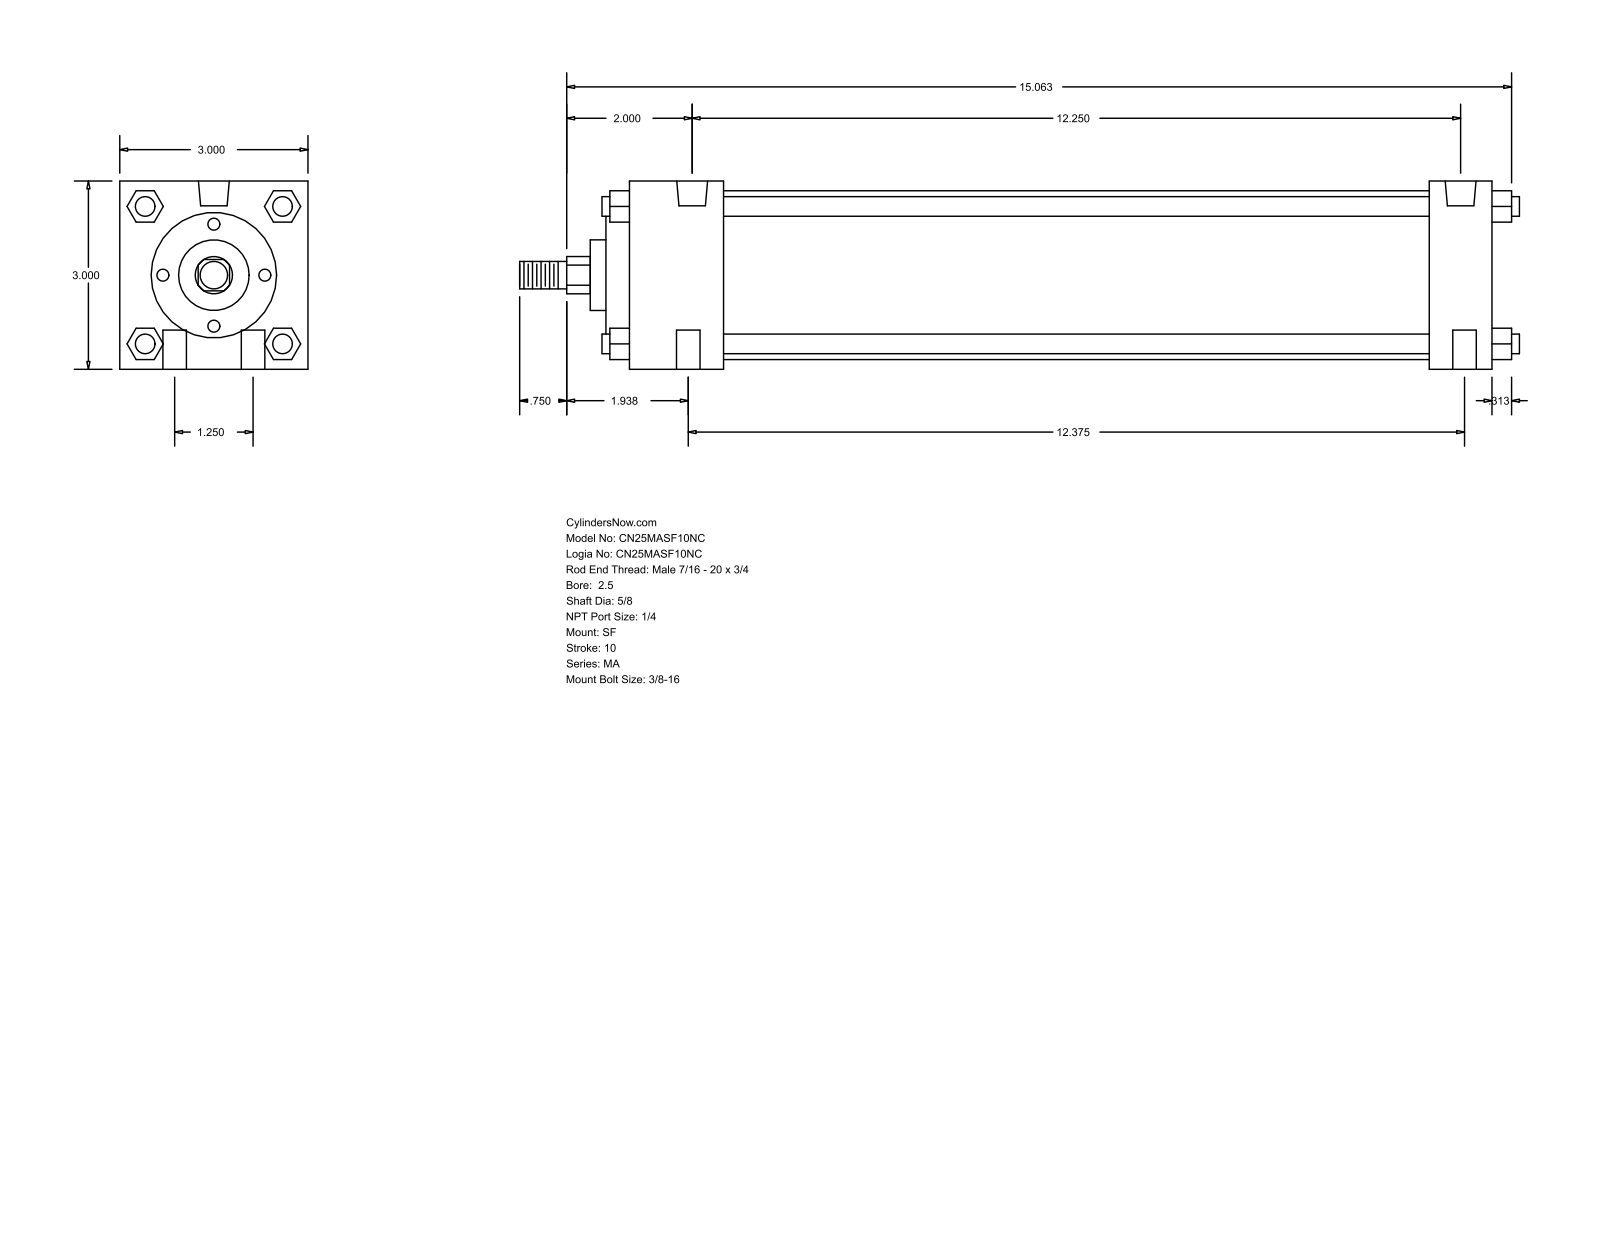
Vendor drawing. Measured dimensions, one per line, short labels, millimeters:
name: MA_SF__0250_0.625
written by: GSSL Pune (CONFIG_CONTROL_DESIGN)
unit: mm
bodies: 0 solids, 126 faces (95 planar, 31 cylindrical, 0 other)
size: 404.81 × 76.2 × 76.2
holes: 4× ⌀9.53, 2× ⌀7.94, 2× ⌀12.49
bosses: 4× ⌀7.94, 1× ⌀68.33, 1× ⌀50.8, 1× ⌀28.57, 1× ⌀15.88, 1× ⌀11.11
rounds: 1× R7.54
face distances: 76.2, 349.25, 25.4, 323.85, 38.1, 285.75, 311.15, 12.7, 9.52, 47.62
hole spacings: 15.96, 313.14, 31.76, 311.15, 314.33, 315.93
